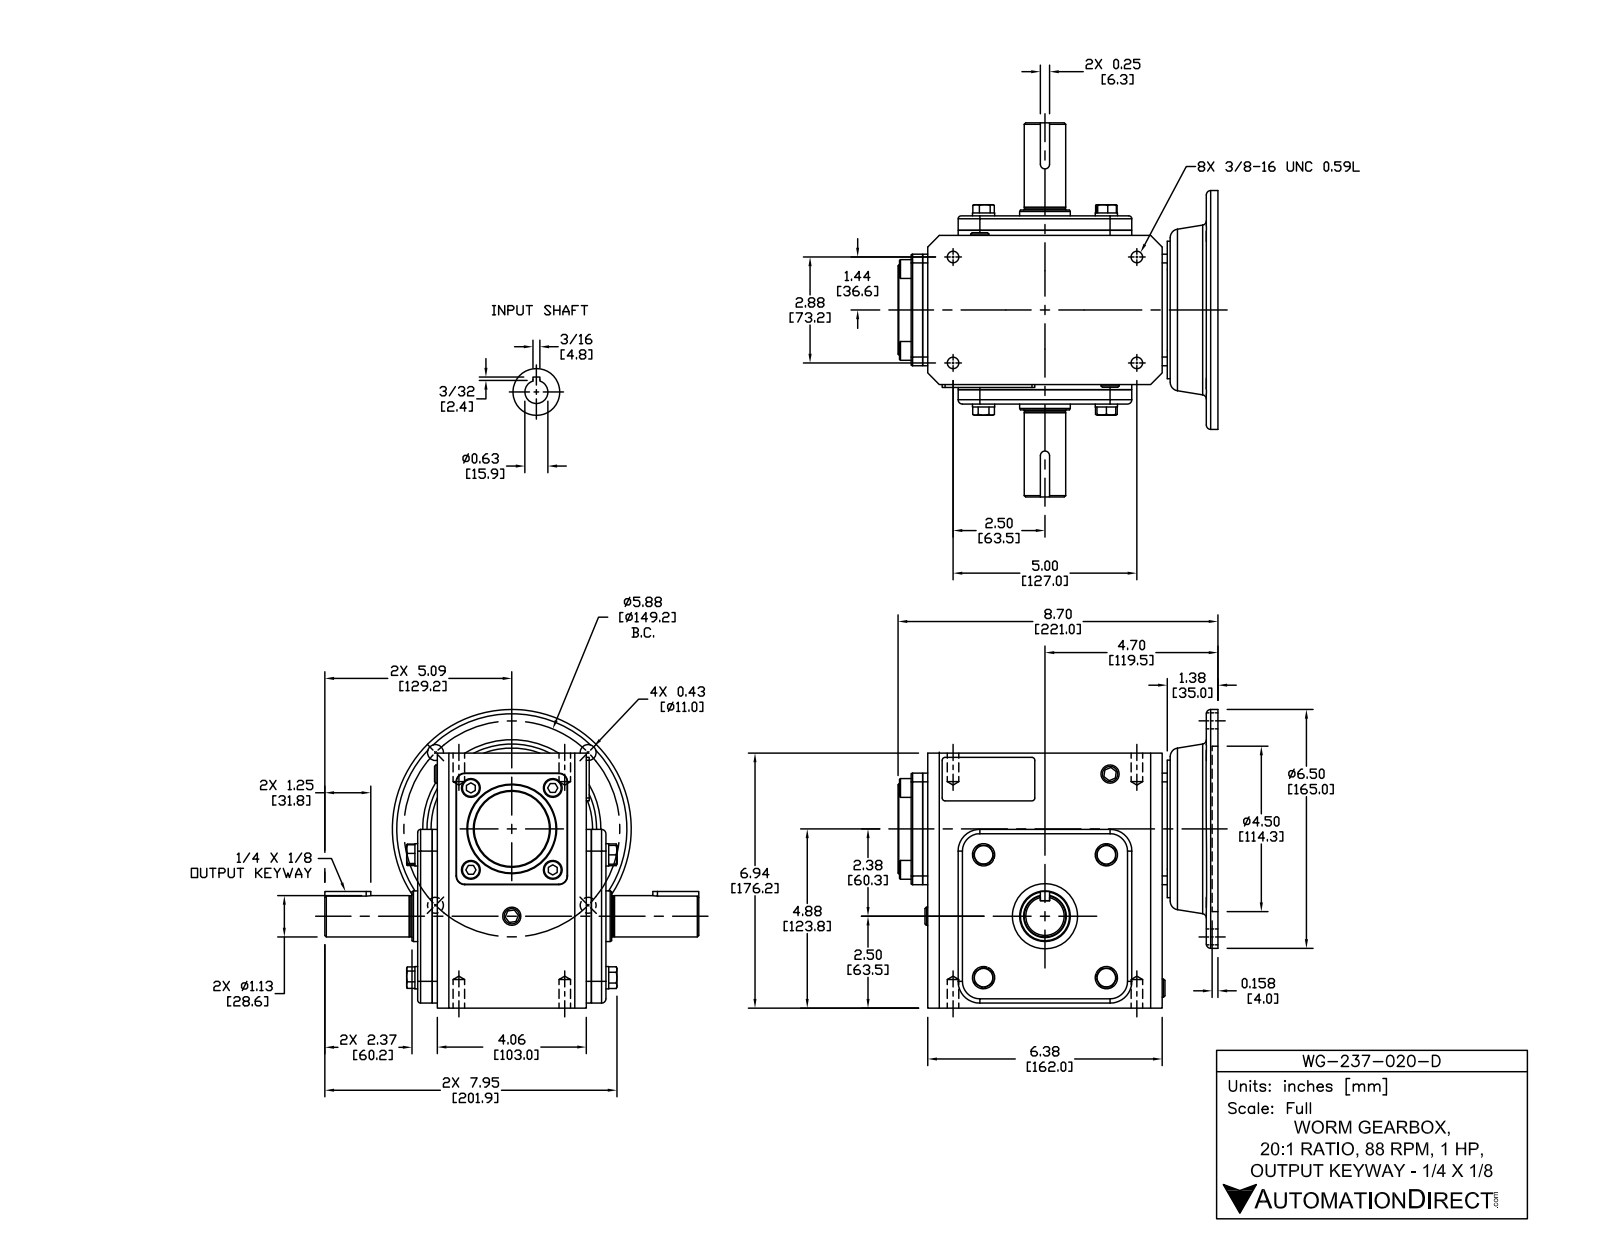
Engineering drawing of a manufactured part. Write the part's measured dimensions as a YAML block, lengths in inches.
part_name: "WG-237-020-D"
step_written_by: "SolidWorks 2015 (CONFIG_CONTROL_DESIGN)"
units: inches
bodies: {solids: 39, faces: 572, planar: 308, cylindrical: 164, other: 100}
overall_size: [10.173, 8.701, 8.123]
volume: 226.1
surface_area: 525.6
round_holes:
  - {diameter: 0.313, count: 4}
  - {diameter: 0.406, count: 4}
  - {diameter: 0.591, count: 1}
  - {diameter: 0.625, count: 1}
  - {diameter: 1.378, count: 1}
  - {diameter: 1.457, count: 1}
  - {diameter: 1.772, count: 1}
  - {diameter: 3.819, count: 1}
  - {diameter: 4.5, count: 1}
round_bosses_or_shafts:
  - {diameter: 0.606, count: 4}
  - {diameter: 0.512, count: 4}
  - {diameter: 6.496, count: 1}
  - {diameter: 3.74, count: 1}
  - {diameter: 2.441, count: 1}
  - {diameter: 2.047, count: 1}
  - {diameter: 1.181, count: 1}
  - {diameter: 1.142, count: 1}
partial_cylinders:
  - {radius: 0.079, count: 8}
  - {radius: 0.118, count: 8}
  - {radius: 0.236, count: 6}
  - {radius: 0.591, count: 4}
  - {radius: 0.02, count: 2}
  - {radius: 0.039, count: 2}
  - {radius: 0.125, count: 2}
face_to_face_distances: [0.138, 4.331, 4.724, 0.394, 0.531, 4.587, 4.193, 6.516, 6.937, 0.315]
hole_center_spacings: [2.937, 2.098, 2.88, 4.154, 4.154, 4.913, 5, 5.77]
